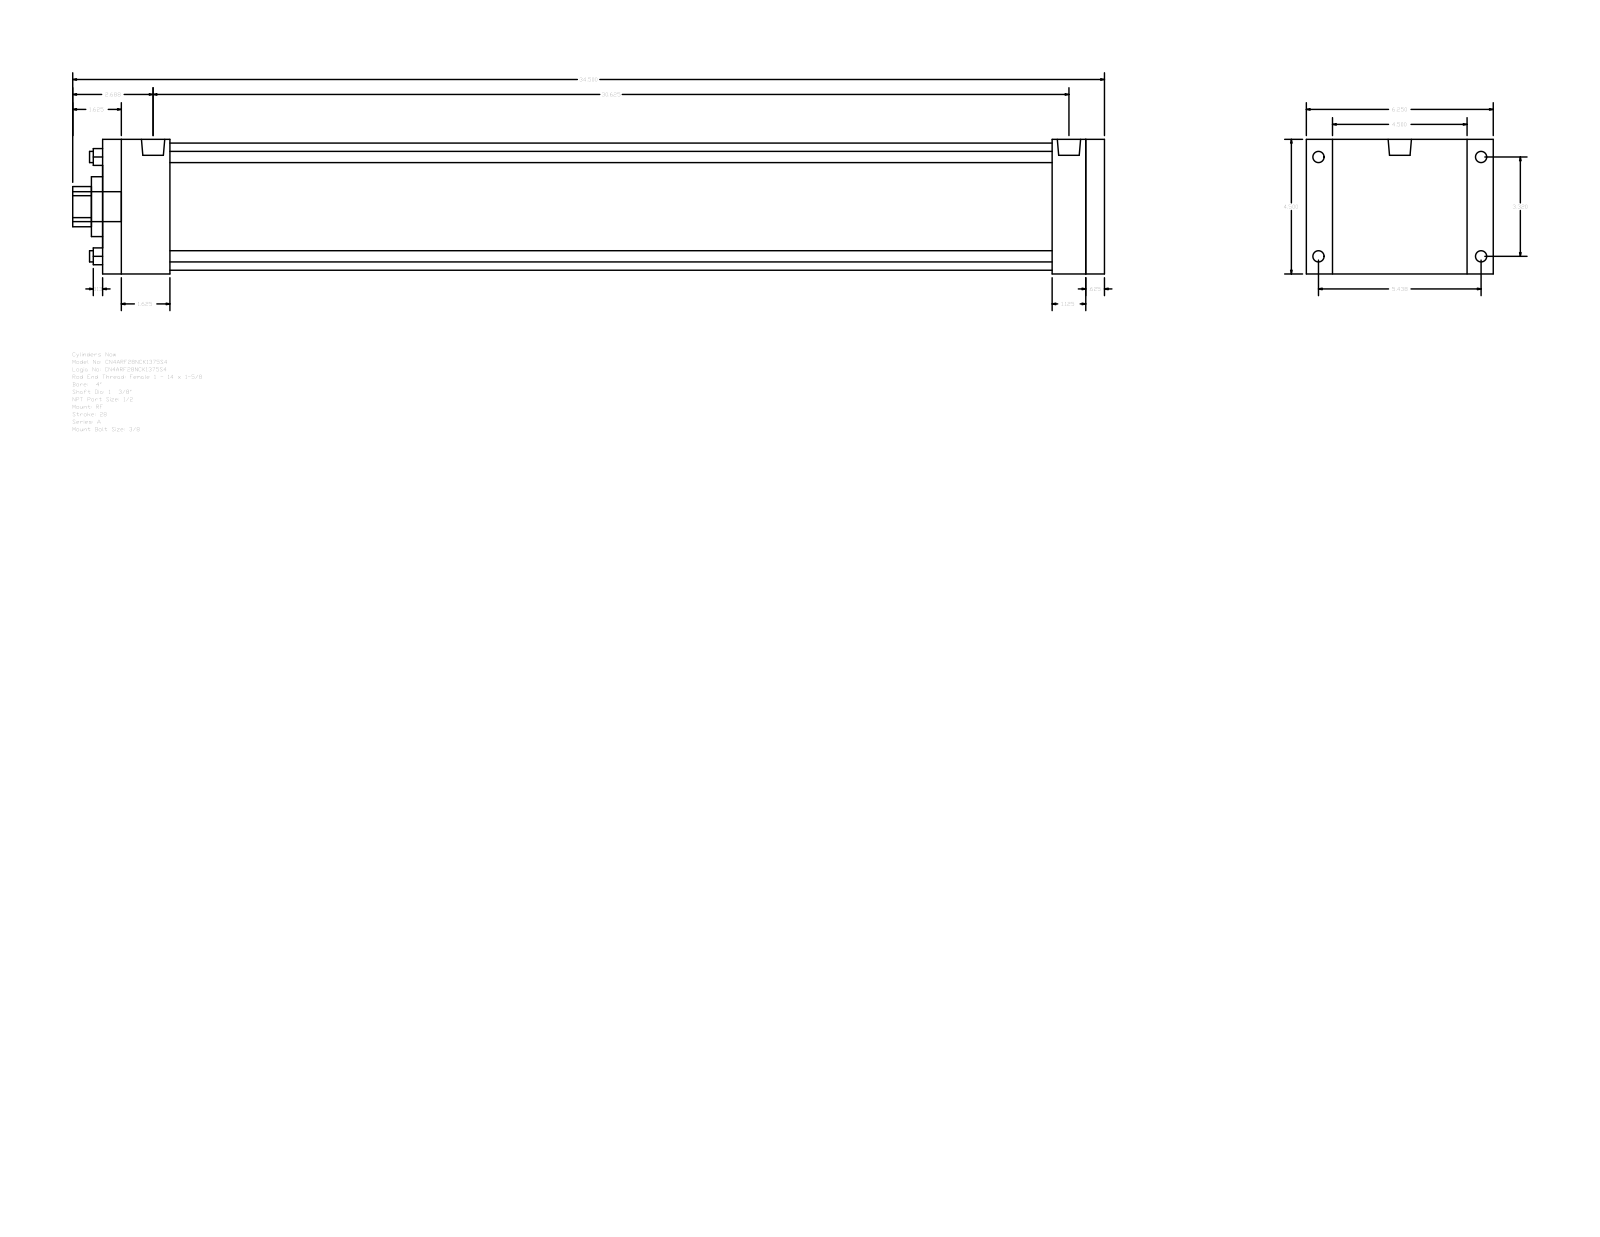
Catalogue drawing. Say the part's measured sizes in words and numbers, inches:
The part is named "A_RF__0400_1.375". Its 3-D file was written by "GSSL Pune (CONFIG_CONTROL_DESIGN)". It is 0 solids with 92 faces: 64 planar, 28 cylindrical and 0 other. Overall it measures 34.5 by 6.25 by 4.5 inches. Round holes: 4 of diameter 0.375, 1 of diameter 1.375, 1 of diameter 2, 1 of diameter 4.25. Round bosses or shafts: 4 of diameter 0.375, 4 of diameter 0.344, 2 of diameter 0.778, 1 of diameter 1. Partial cylindrical surfaces (rounded edges, fillets, slot ends): 1 of radius 0.672. The main face-to-face distances are 4.5, 33.5, 0.625, 32.875, 1.125, 0.875, 5.375, 31.75, 1.75, 2.25. The hole center spacings are 2.347, 3.32, 4.695.
